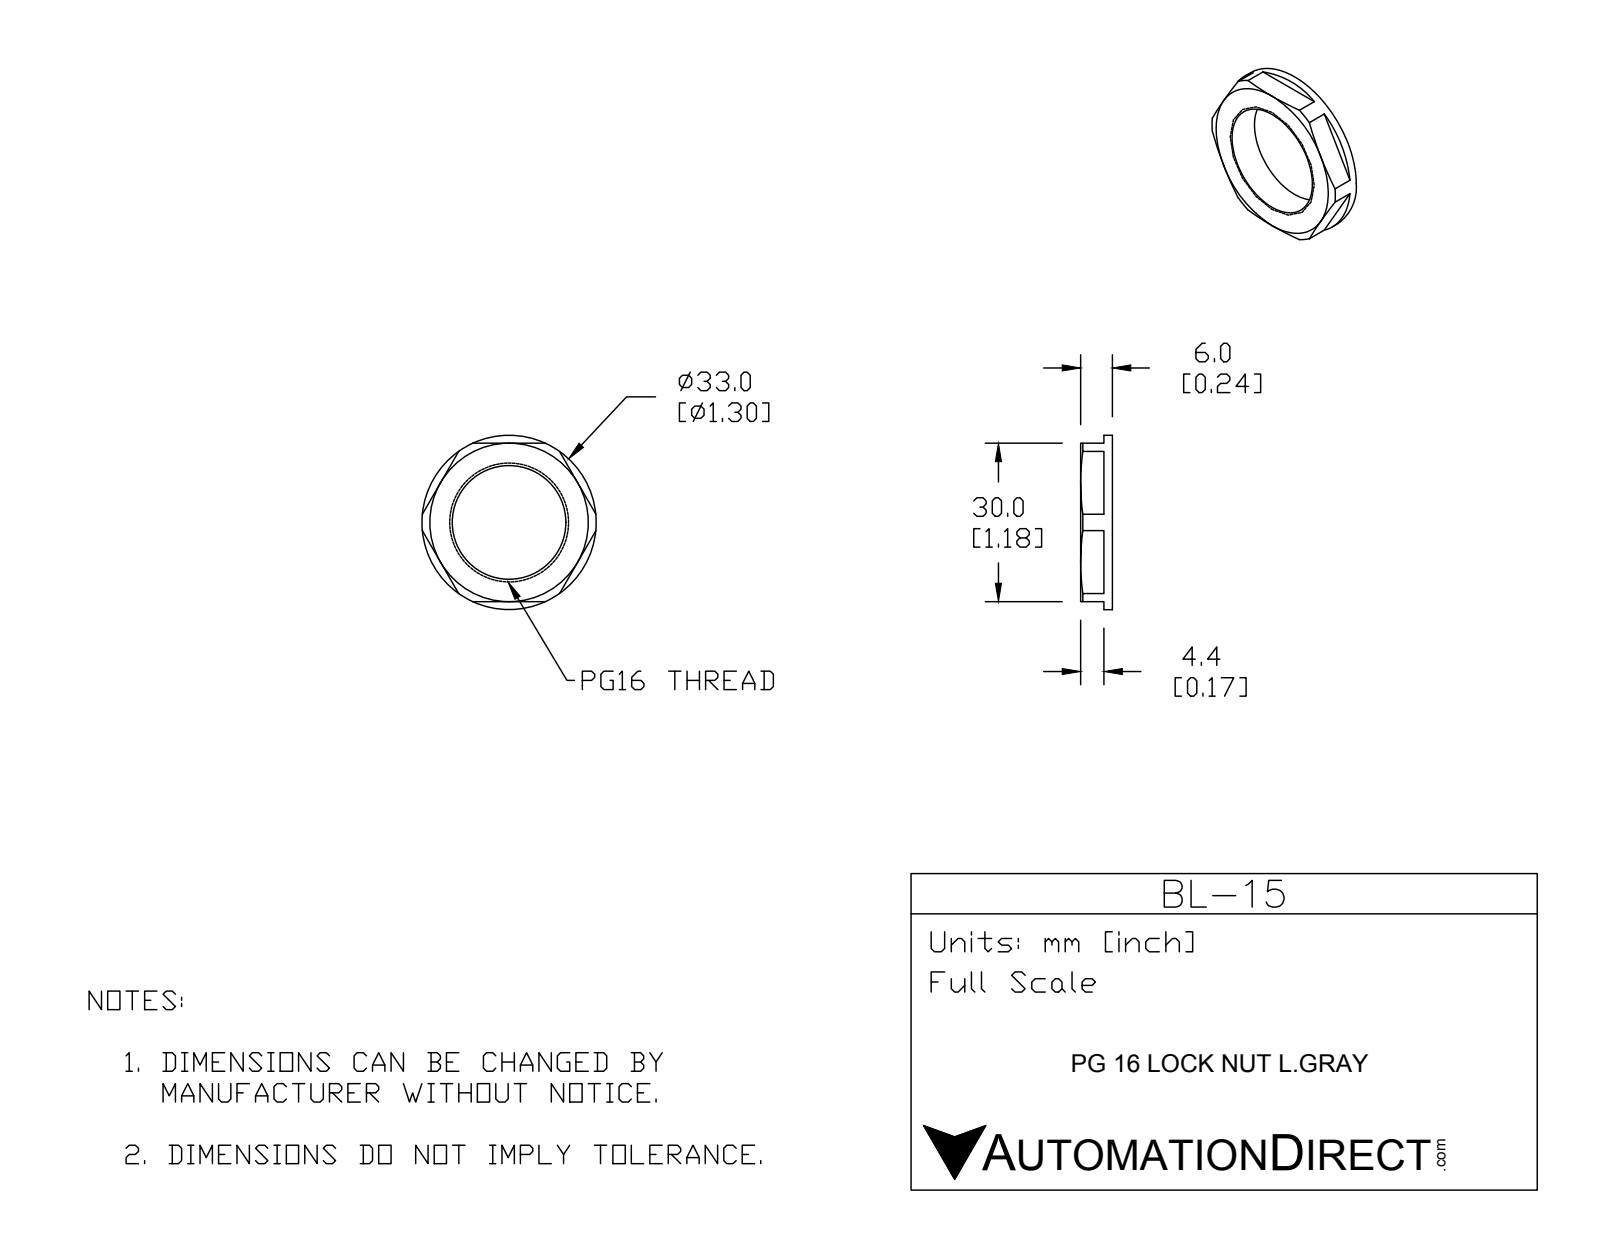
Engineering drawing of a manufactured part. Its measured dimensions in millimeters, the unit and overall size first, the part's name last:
Units: millimetres
Overall size (bounding box): 33 × 33 × 6
Round holes (diameter × count): ⌀1.5 ×3, ⌀21.5 ×1
Round bosses / shafts (diameter × count): ⌀33 ×1
Main face-to-face distances: 6, 30, 1.6, 4.4, 1.3, 5.7
Hole centre spacings: 15.05, 26.06, 15.04, 26.07
Volume: 2 575 mm³ · Surface area: 1 988 mm²
Bodies: 1 solid, 33 faces (17 planar, 10 cylindrical, 6 other)
Part name (STEP PRODUCT): BL-15
STEP written by: SolidWorks 2015 (CONFIG_CONTROL_DESIGN)
